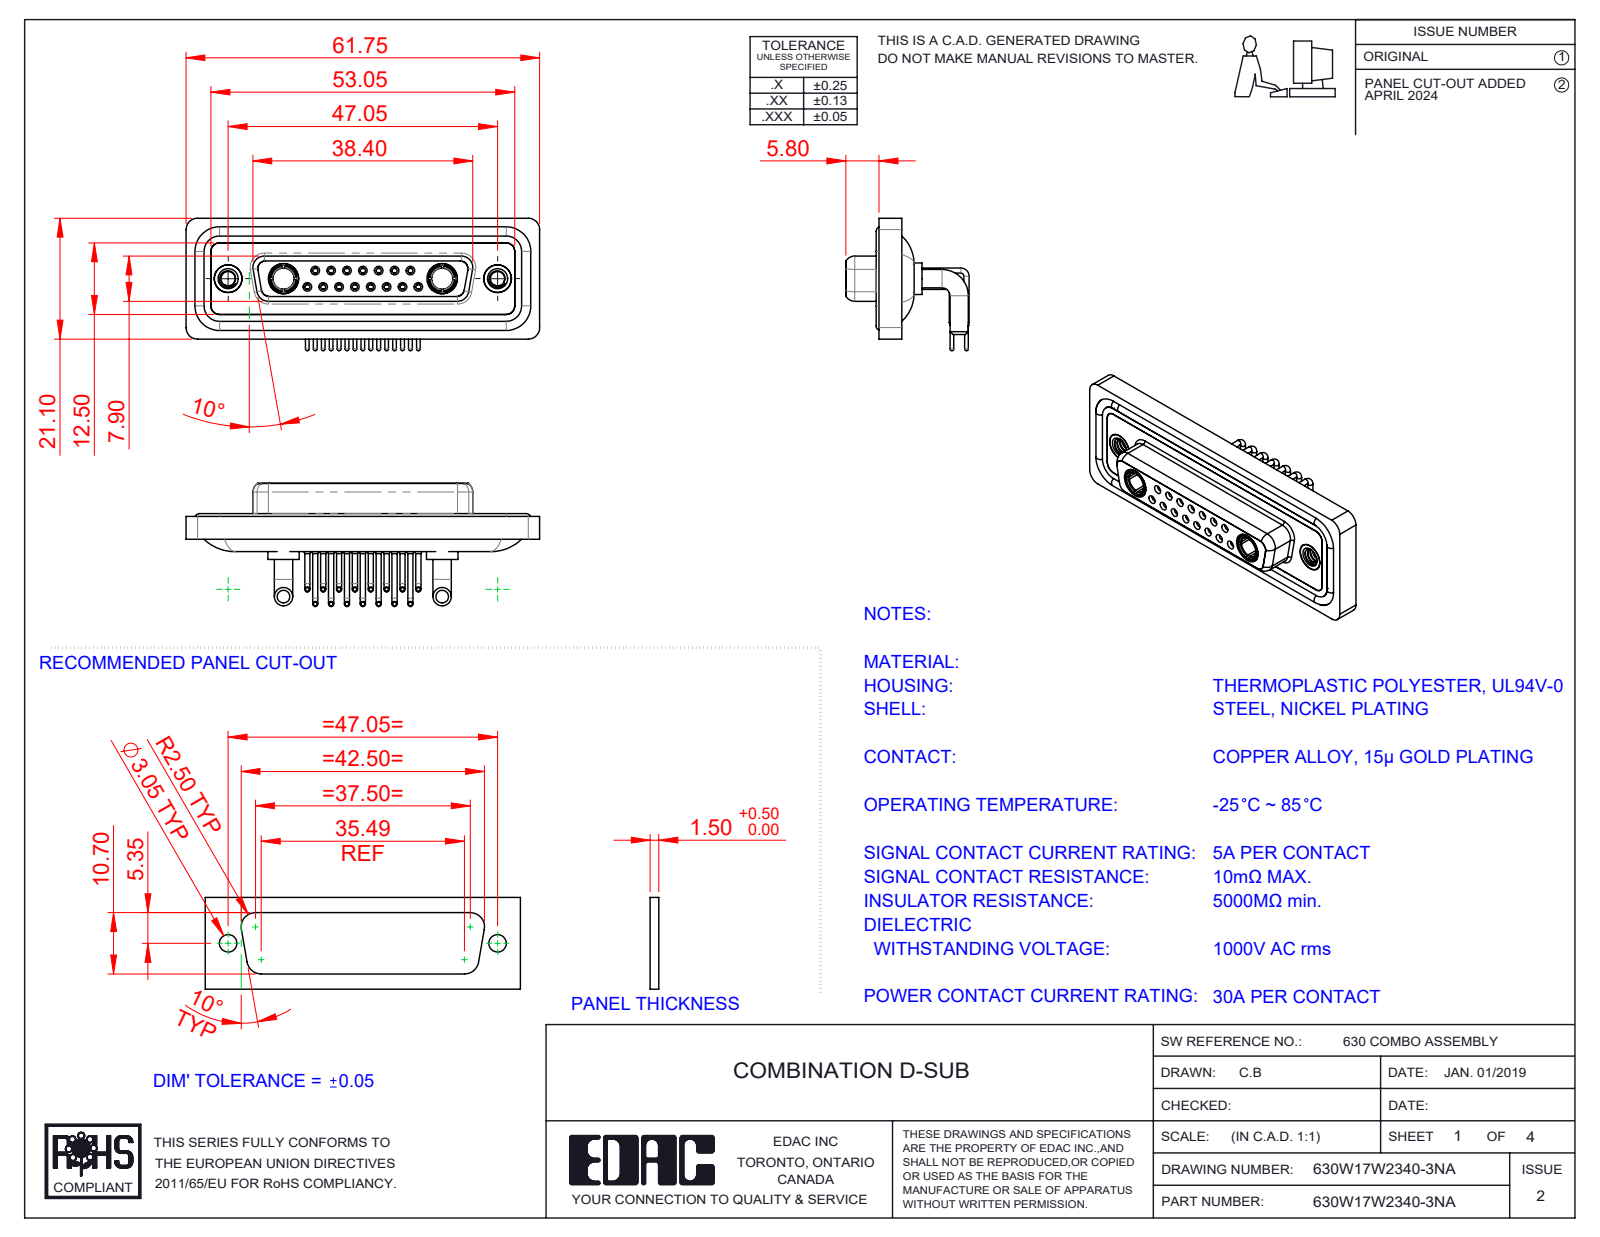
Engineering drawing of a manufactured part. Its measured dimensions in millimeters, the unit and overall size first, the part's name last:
Units: millimetres
Overall size (bounding box): 61.75 × 23.12 × 21.53
Round holes (diameter × count): ⌀0.9 ×15, ⌀1.1 ×15, ⌀1.5 ×15, ⌀2 ×15, ⌀1.6 ×8, ⌀1.7 ×7, ⌀4.85 ×4, ⌀2.5 ×2, ⌀3.7 ×2, ⌀4 ×2, ⌀4.05 ×2, ⌀5 ×2
Round bosses / shafts (diameter × count): ⌀0.9 ×15, ⌀0.65 ×15, ⌀1.6 ×11, ⌀3.2 ×4, ⌀5.5 ×2, ⌀5.2 ×2, ⌀4.96 ×2, ⌀4.95 ×2
Partial cylindrical surfaces — rounded edges, fillets, slot ends (radius × count): R1.5 ×18, R2 ×18, R1.35 ×8, R1.6 ×8, R0.25 ×4, R0.5 ×4, R0.6 ×4, R0.65 ×4
Main face-to-face distances: 0.4, 1.8, 4.1, 1.1, 1.6, 3.1, 2.5, 1.5, 3.7, 1.4
Hole centre spacings: 3.16, 2.77, 5.54, 8.31, 5.04, 7.49, 11.08, 5.03
Volume: 8 535 mm³ · Surface area: 14 570 mm²
Bodies: 26 solids, 1331 faces (388 planar, 581 cylindrical, 362 other)
Part name (STEP PRODUCT): 630Combo Shell Rear_25 Contacts; Power Socket_30A RA; 630Combo Shell Front_25 Contacts; 630Combo Contact Row 1_50 Contacts (+5 more)
STEP written by: SolidWorks 2023 (CONFIG_CONTROL_DESIGN)
